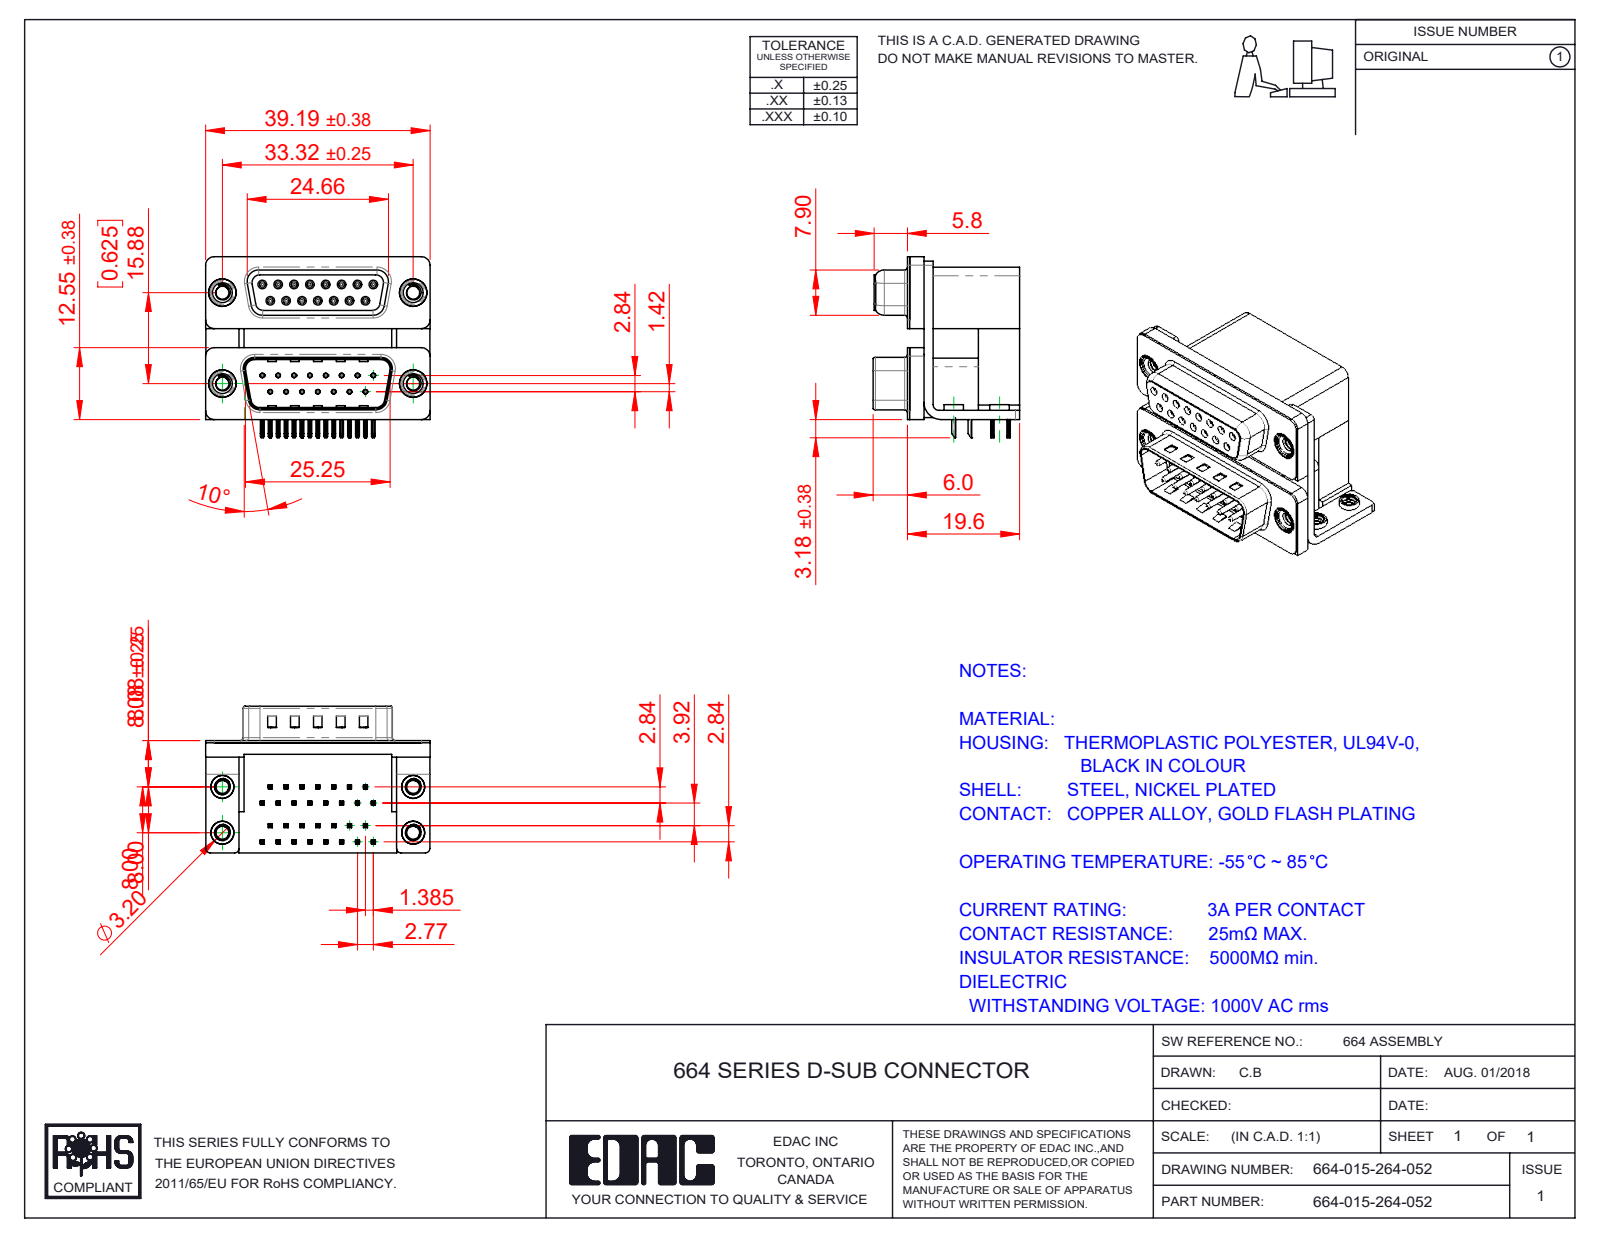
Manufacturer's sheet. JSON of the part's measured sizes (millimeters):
{"part_name": "664 Housing Spacer_15 Contacts L; 664 Contact Top Lower; 664 Shell Receptacle_15 Contacts; 664 Contact Top Upper_L (+8 more)", "step_written_by": "SolidWorks 2020 (CONFIG_CONTROL_DESIGN)", "units": "millimeters", "bodies": {"solids": 45, "faces": 4052, "planar": 2027, "cylindrical": 1090, "other": 935}, "overall_size": [39.19, 31.61, 25.6], "volume_mm3": 14572, "surface_area_mm2": 16511, "round_holes": [[0.8, 30], [0.35, 15], [0.9, 15], [2.26, 8], [2.75, 4], [3.2, 4], [3.5, 4], [4, 4], [4.8, 4], [5, 4]], "round_bosses_or_shafts": [[1.2, 15], [0.75, 15], [4.9, 4], [4.75, 4], [4, 4], [3.9, 4], [3.4, 4]], "partial_cylinders_radius": [[0.1, 120], [0.15, 60], [0.25, 60], [0.12, 30], [0.35, 30], [1.5, 16], [0.34, 15], [0.5, 12]], "face_to_face_distances": [0.4, 19.2, 16.7, 2.5, 7.2, 12, 9.5, 2.19, 10.7, 2.9], "hole_center_spacings": [3.16, 2.77, 16.12, 5.54, 16.82, 8.31, 15.88, 17.92]}
